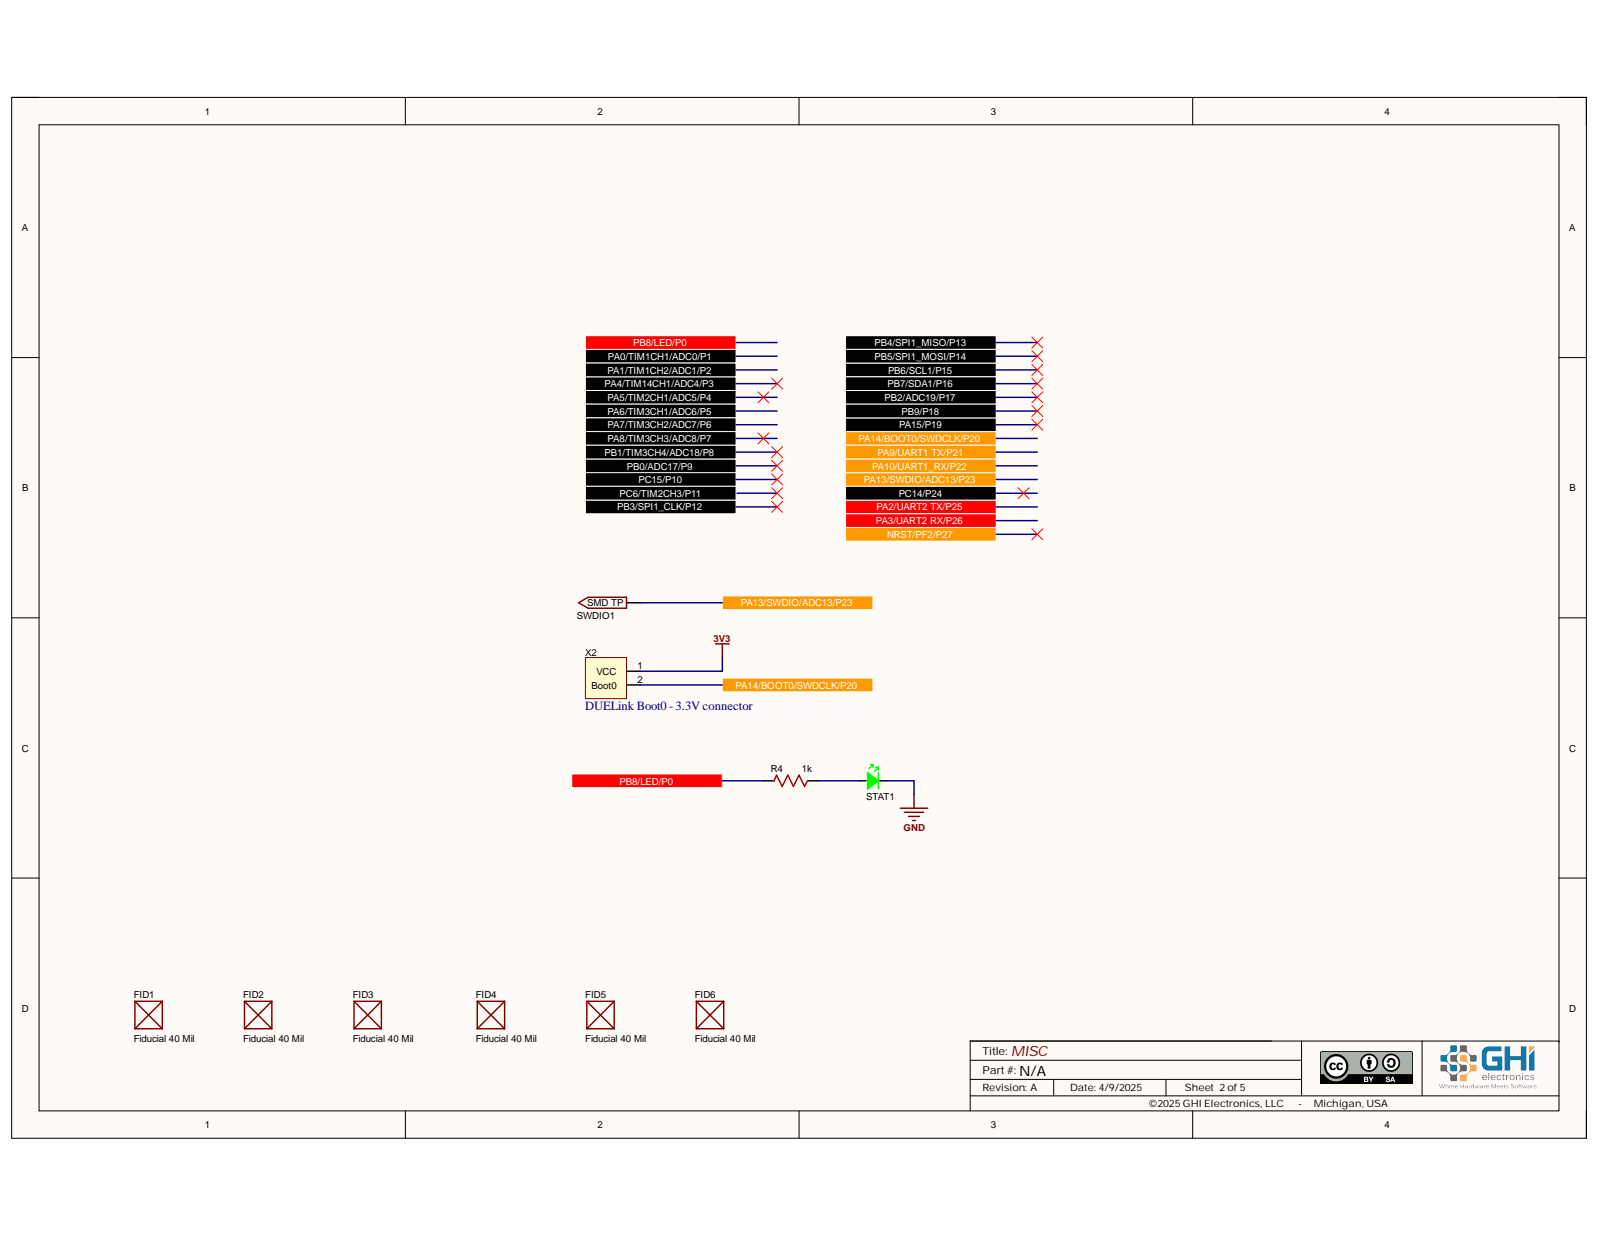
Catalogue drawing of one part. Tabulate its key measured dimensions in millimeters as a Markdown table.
| quantity | value |
| --- | --- |
| part name | PCB; Board; X1; 691102710003 (+6 more) |
| STEP written by | Open CASCADE 7.5 (AUTOMOTIVE_DESIGN) |
| units | millimeters |
| bodies | 124 solids, 2328 faces (1632 planar, 339 cylindrical, 357 other) |
| overall size | 32 × 22 × 13.4 |
| volume | 1 969 mm³ |
| surface area | 4 175 mm² |
| round holes (diameter × count) | 3 × 7, 0.6 × 3, 1.3 × 3, 2 × 3, 2.75 × 3, 3.5 × 3, 1.02 × 2 |
| round bosses / shafts (diameter × count) | 2.5 × 3, 1 × 3 |
| partial cylindrical surfaces (radius × count) | 0.12 × 35, 0.15 × 14, 0.15 × 14, 0.8 × 12, 0.2 × 7, 0.13 × 6, 0.2 × 6, 0.33 × 4 |
| main face-to-face distances | 1.6, 5, 4, 5.5, 9, 14, 0.5, 0.85, 4.5, 4.7 |
| hole center spacings | 5, 5.94, 3.2, 10, 4.25, 7.92, 9.15, 9.45 |
